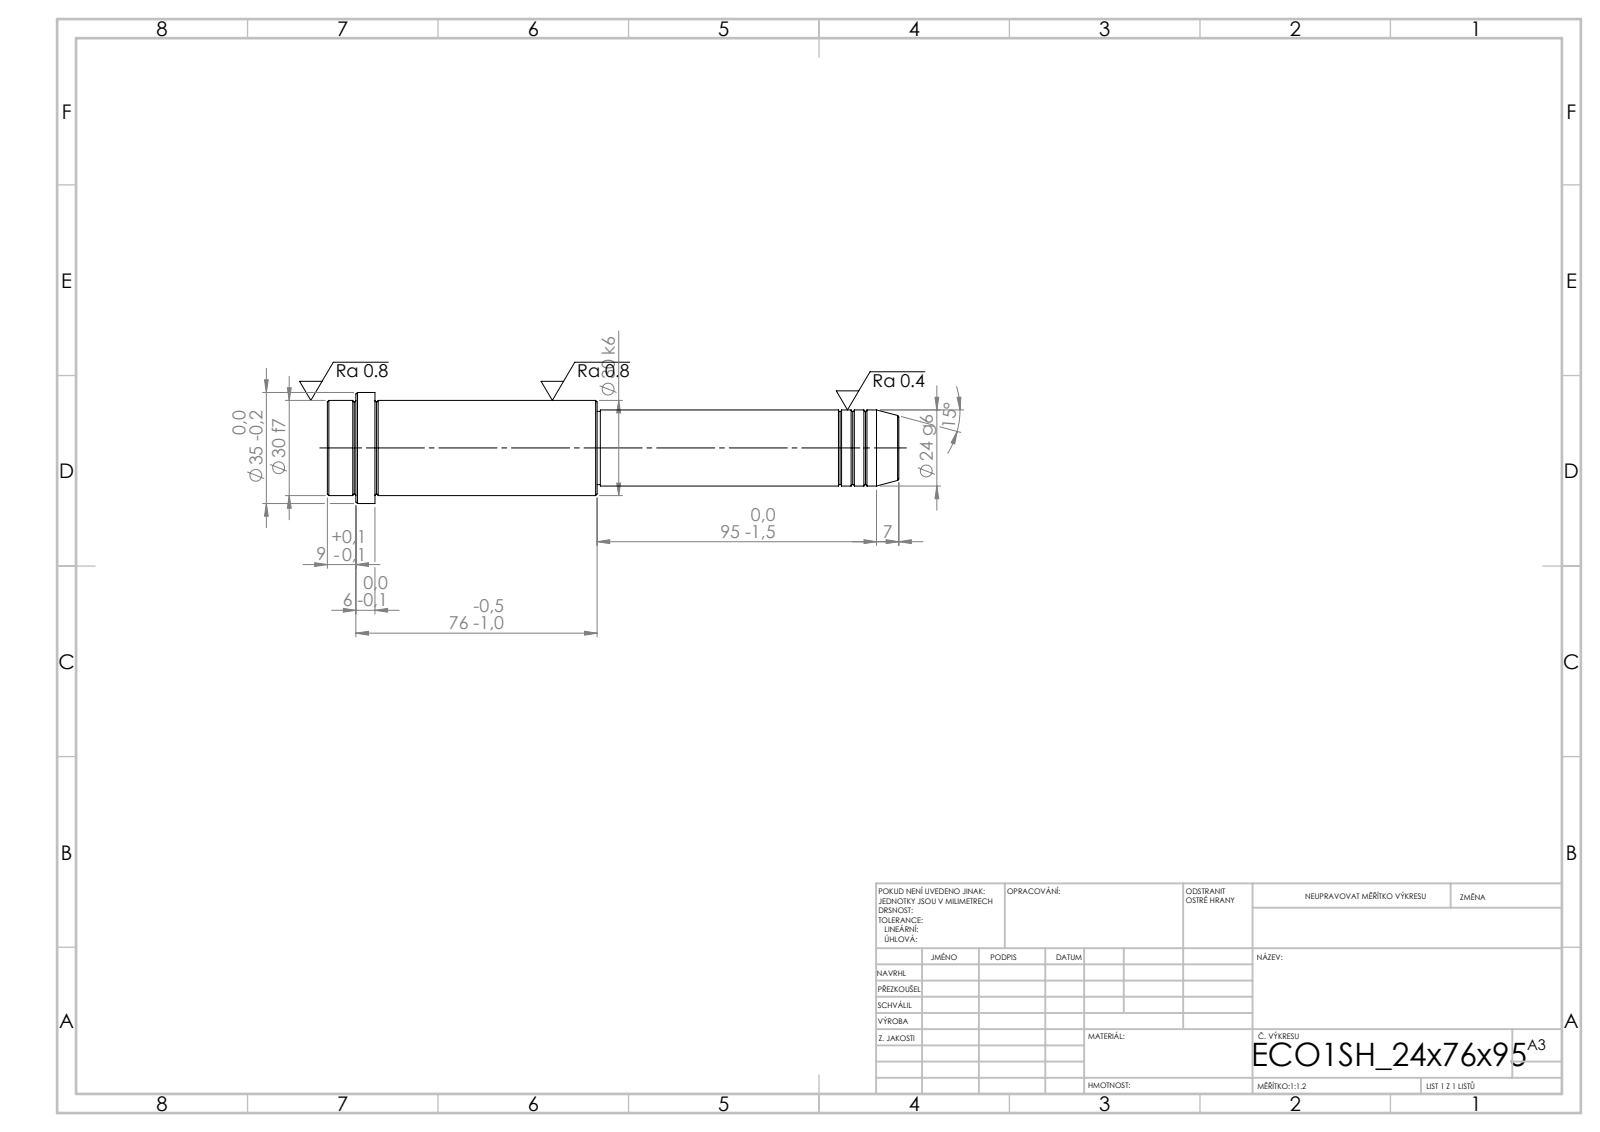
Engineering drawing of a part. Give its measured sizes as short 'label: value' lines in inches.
written by: SolidWorks 2019 (CONFIG_CONTROL_DESIGN)
unit: in
bodies: 1 solid, 52 faces (6 planar, 16 cylindrical, 30 other)
size: 7.087 × 1.378 × 1.378
volume: 6.34 in³; area: 26.71 in²
bosses: 1× ⌀1.378, 1× ⌀1.181, 1× ⌀0.945, 1× ⌀0.906
face distances: 7.087, 6.496, 0.591, 3.74, 2.756, 3.346, 6.732, 2.992, 0.236, 0.354
